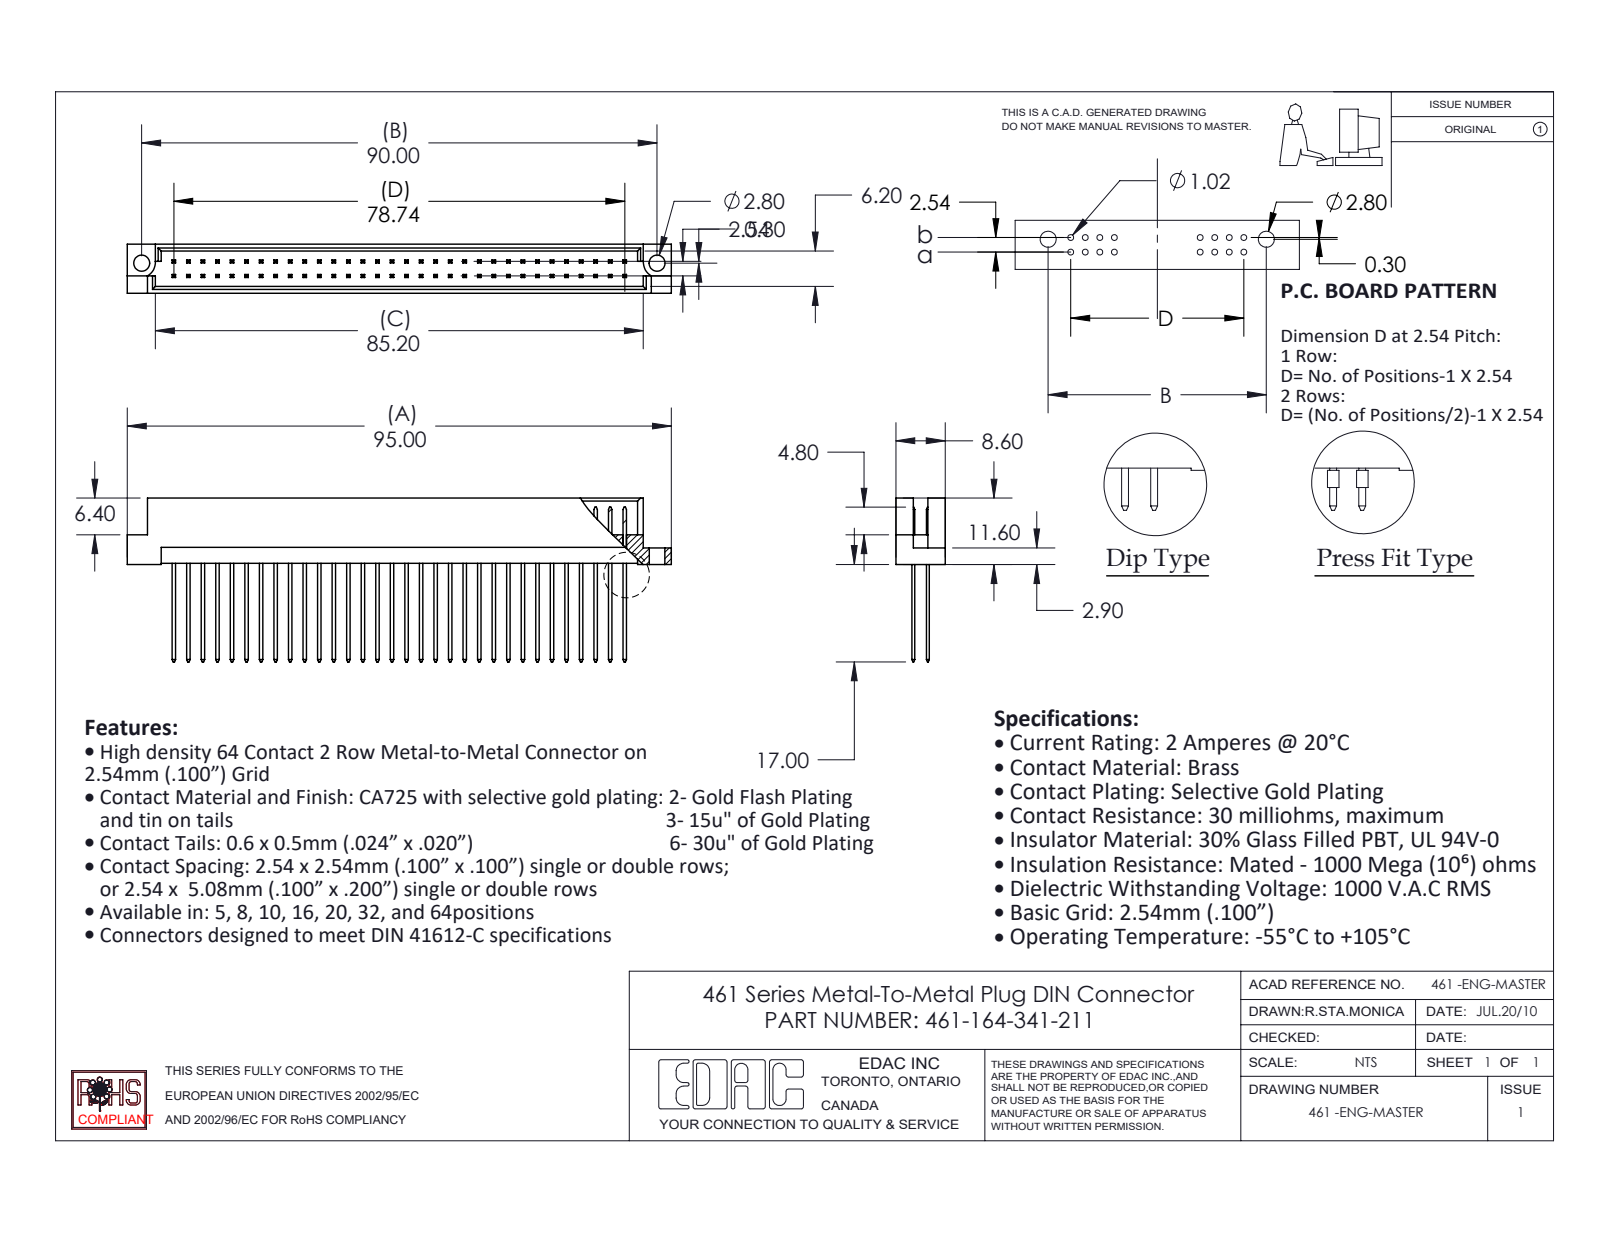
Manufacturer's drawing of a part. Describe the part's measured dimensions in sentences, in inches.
The part is named "461-164-341-211; 461-290_41; 461 Part_64". Its 3-D file was written by "SolidWorks 2020 (CONFIG_CONTROL_DESIGN)". It is 65 solids with 1201 faces: 1194 planar, 7 cylindrical and 0 other. Overall it measures 3.74 by 1.126 by 0.339 inches. Its volume is 0.315 cubic inches and its surface area 14.64 square inches. Round holes: 2 of diameter 0.11. Partial cylindrical surfaces (rounded edges, fillets, slot ends): 2 of radius 0.11. The main face-to-face distances are 0.1, 0.047, 0.291, 0.109, 0.129, 0.209, 0.229, 0.062, 0.082, 0.162. The hole center spacings are 3.543.
